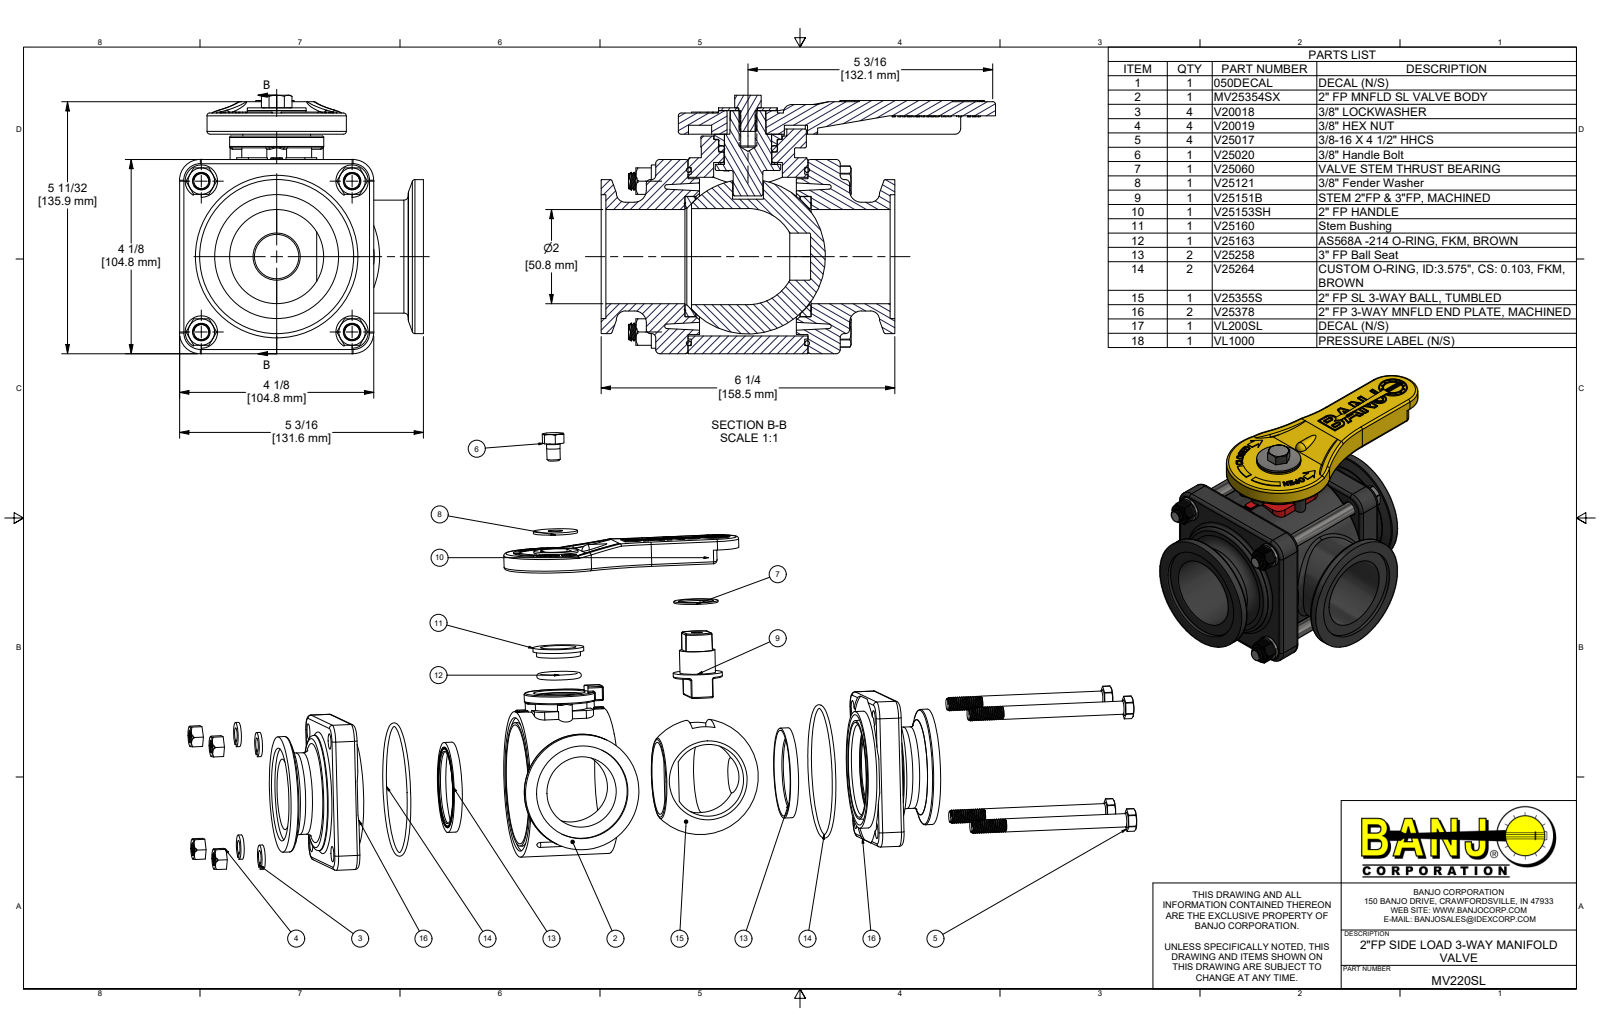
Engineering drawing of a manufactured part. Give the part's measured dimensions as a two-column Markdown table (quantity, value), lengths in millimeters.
| quantity | value |
| --- | --- |
| part name | MV25354SX; V20018; V20019; V25017 (+8 more) |
| STEP written by | Autodesk Inventor 2014 (AUTOMOTIVE_DESIGN) |
| units | millimeters |
| bodies | 27 solids, 2430 faces (1317 planar, 472 cylindrical, 641 other) |
| overall size | 212.85 × 139.43 × 131.59 |
| volume | 916 171 mm³ |
| surface area | 280 423 mm² |
| round holes (diameter × count) | 4.33 × 12, 7.81 × 4, 9.78 × 4, 11.13 × 4, 25.4 × 2, 50.8 × 2, 51.82 × 2, 7.8 × 1, 10.31 × 1, 13.83 × 1, 19.55 × 1, 25.81 × 1 |
| round bosses / shafts (diameter × count) | 8.24 × 60, 9.52 × 5, 17.46 × 4, 83.06 × 2, 88.9 × 1, 84.07 × 1, 75.18 × 1, 64.77 × 1 |
| partial cylindrical surfaces (radius × count) | 0.76 × 18, 2.29 × 18, 0.81 × 10, 1.59 × 8, 4.12 × 8, 1.52 × 6, 3.05 × 5, 5.33 × 4 |
| main face-to-face distances | 17.4, 82.16, 2.54, 45.21, 64.76, 110.75, 104.78, 15.74, 83.82, 1.66 |
| hole center spacings | 50.22, 71.02, 97.02, 25.99, 28.77, 54.26, 76.38, 86.98 |
